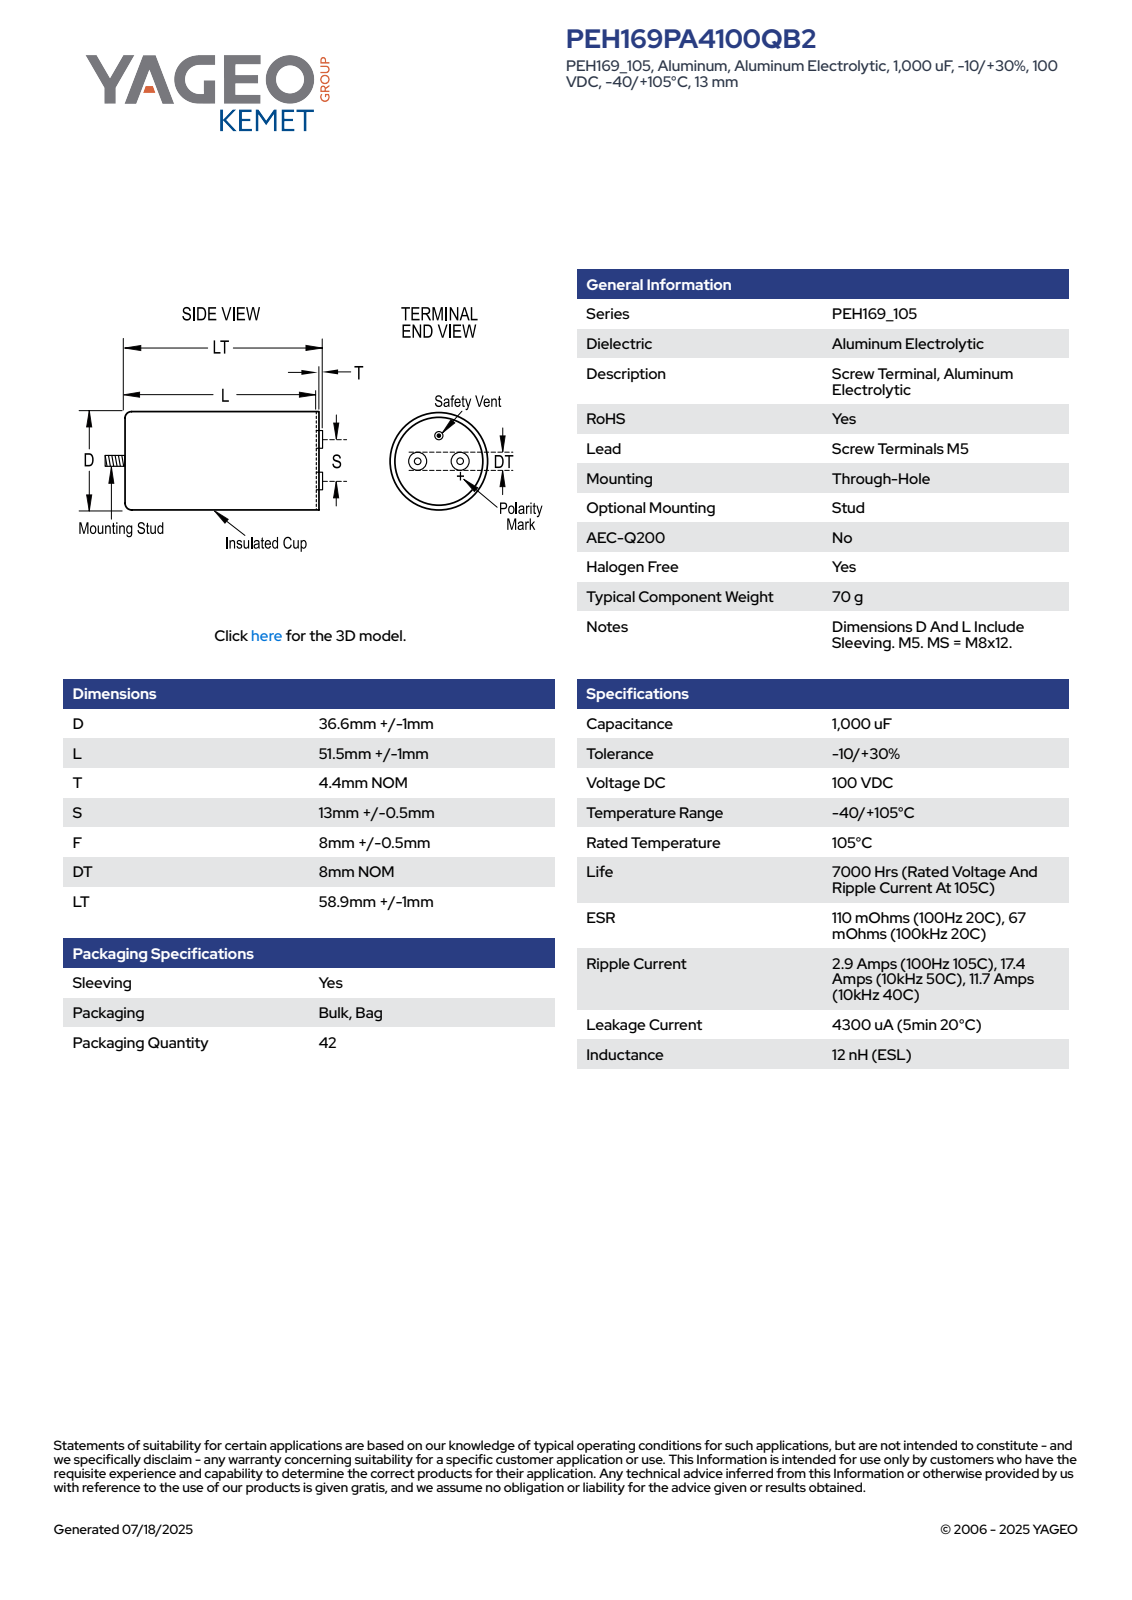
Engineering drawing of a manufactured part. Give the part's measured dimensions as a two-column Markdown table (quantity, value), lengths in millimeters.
| quantity | value |
| --- | --- |
| part name | CARCS_D37.6L52.5S13T4.4; Can_Round_5; Round_Terminal; Stud8 |
| STEP written by | SolidWorks 2014 (AUTOMOTIVE_DESIGN) |
| units | millimeters |
| bodies | 4 solids, 147 faces (54 planar, 61 cylindrical, 32 other) |
| overall size | 71.9 × 37.6 × 37.6 |
| volume | 59 299 mm³ |
| surface area | 10 113 mm² |
| round holes (diameter × count) | 5 × 2, 35.6 × 1 |
| round bosses / shafts (diameter × count) | 8 × 3, 37.6 × 1, 7.7 × 1 |
| partial cylindrical surfaces (radius × count) | 18.79 × 1 |
| main face-to-face distances | 52.5, 3, 55.5, 4.4, 7.4, 59.9, 1, 71.9, 67.5, 64.5 |
| hole center spacings | 6.5, 13 |
